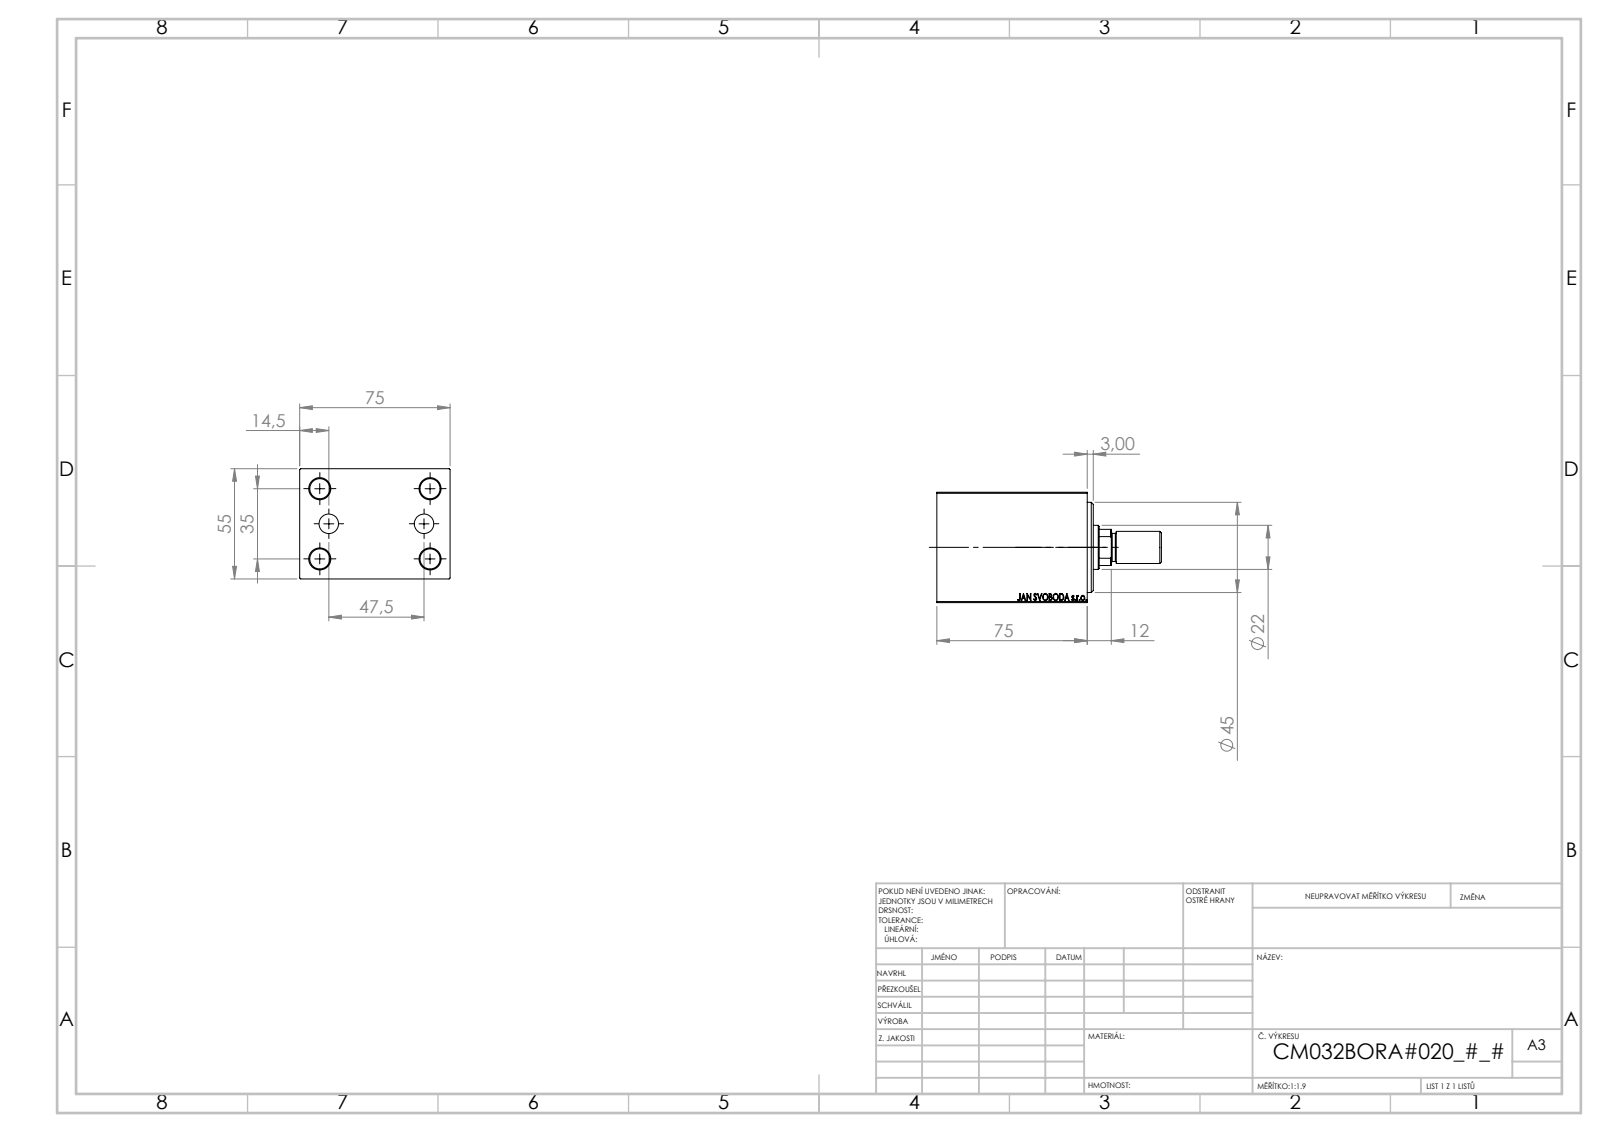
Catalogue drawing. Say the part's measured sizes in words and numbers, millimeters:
The part is named "V450CM_B_Body; V450CM_VC_B; V450CM_MALE_METRIC; V450CM_B_VCP". Its 3-D file was written by "SolidWorks 2019 (CONFIG_CONTROL_DESIGN)". It is 4 solids with 884 faces: 402 planar, 50 cylindrical and 432 other. Overall it measures 112 by 75 by 55 millimeters. Its volume is 296 817 cubic millimeters and its surface area 55 577 square millimeters. Round holes: 4 of diameter 10, 2 of diameter 9.72, 1 of diameter 10.5, 1 of diameter 22, 1 of diameter 25.5, 1 of diameter 26.5, 1 of diameter 32, 1 of diameter 34, 1 of diameter 45. Round bosses or shafts: 1 of diameter 16, 1 of diameter 14. Partial cylindrical surfaces (rounded edges, fillets, slot ends): 1 of radius 10.5. The main face-to-face distances are 75, 55, 65, 10, 5, 60, 70, 12, 3, 8. The hole center spacings are 32.6, 17.76, 18.07, 35, 53.45, 54.87, 55, 65.19.
